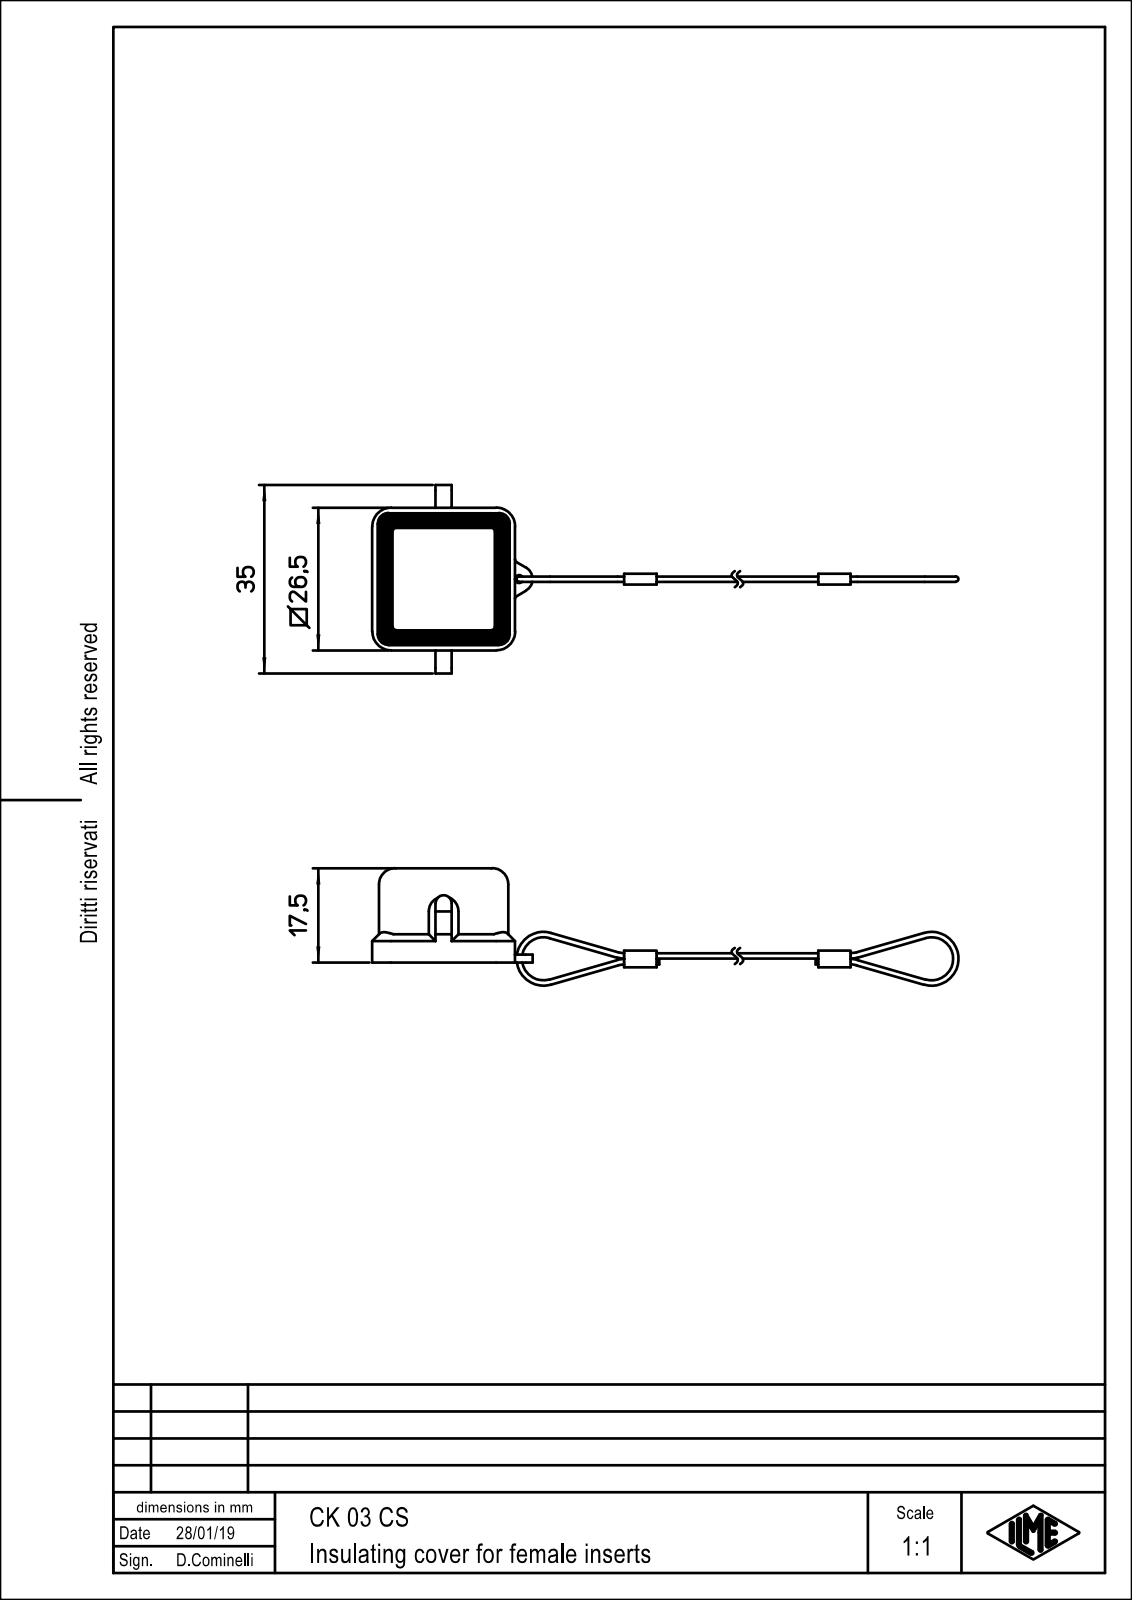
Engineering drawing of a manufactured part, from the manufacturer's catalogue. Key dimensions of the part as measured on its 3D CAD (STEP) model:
Part name (STEP PRODUCT): CK_03_CS
STEP written by: PTC Creo Elements/Direct Modeling 19.0E 27-Jun-2016 (C) Parametric Technology GmbH (AUTOMOTIVE_DESIGN)
Units: millimetres
Bodies: 1 solid, 148 faces (67 planar, 55 cylindrical, 26 other)
Overall size (bounding box): 108.93 × 35 × 21.82
Volume: 3 646 mm³ · Surface area: 4 917 mm²
Round holes (diameter × count): ⌀1.5 ×1
Round bosses / shafts (diameter × count): ⌀1 ×6
Partial cylindrical surfaces — rounded edges, fillets, slot ends (radius × count): R2 ×8, R1 ×6, R0.7 ×4, R3 ×4, R3.2 ×4, R3.5 ×4, R0.5 ×2, R1.5 ×2
Main face-to-face distances: 1.25, 22.75, 24, 21.5, 2.5, 2, 25.25, 16.3, 14.3, 3.75
